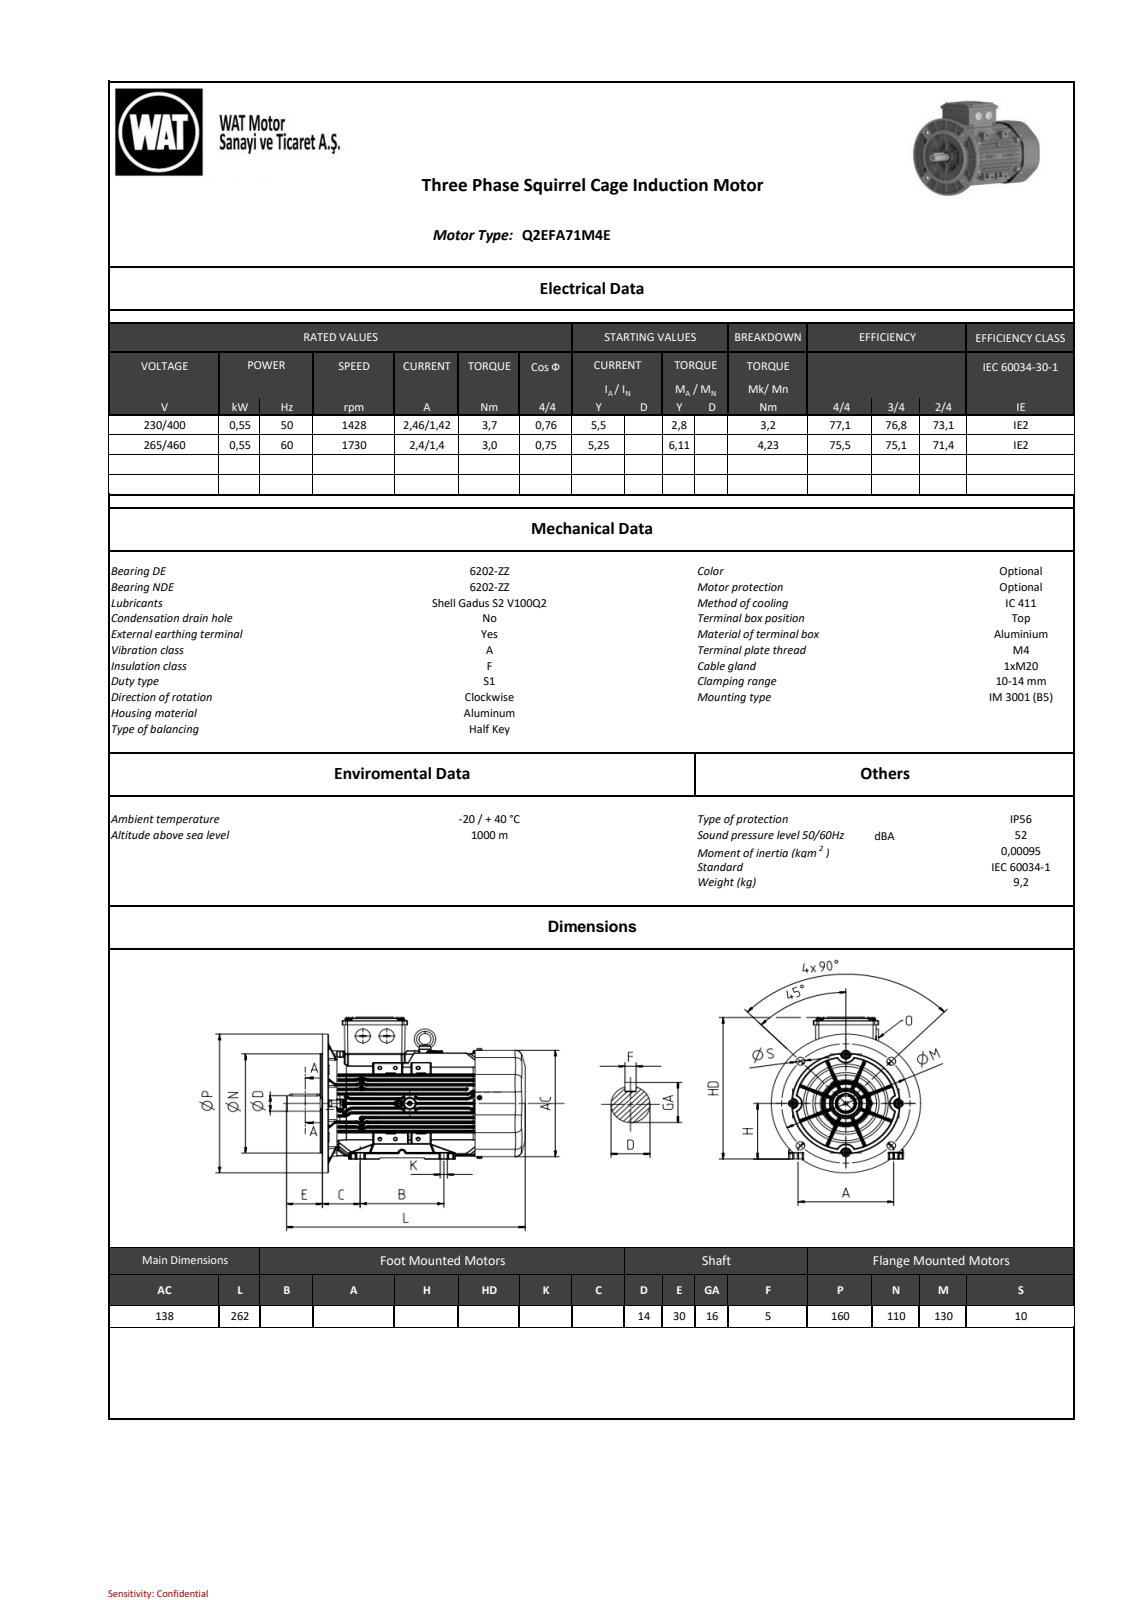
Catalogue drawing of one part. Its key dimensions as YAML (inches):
part_name: "001_objects"
step_written_by: "SIEMENS PLM Software NX2206.8101 (AUTOMOTIVE_DESIGN)"
units: inches
bodies: {solids: 0, faces: 3060, planar: 1377, cylindrical: 779, other: 904}
overall_size: [10.315, 7.367, 6.299]
round_holes:
  - {diameter: 0.13, count: 9}
  - {diameter: 0.144, count: 8}
  - {diameter: 0.098, count: 6}
  - {diameter: 0.197, count: 5}
  - {diameter: 0.157, count: 4}
  - {diameter: 0.177, count: 4}
  - {diameter: 0.183, count: 4}
  - {diameter: 0.189, count: 4}
  - {diameter: 0.394, count: 4}
  - {diameter: 0.118, count: 3}
  - {diameter: 0.146, count: 3}
  - {diameter: 0.181, count: 2}
round_bosses_or_shafts:
  - {diameter: 0.315, count: 8}
  - {diameter: 0.157, count: 8}
  - {diameter: 6.299, count: 1}
  - {diameter: 5.433, count: 1}
  - {diameter: 4.331, count: 1}
  - {diameter: 2.402, count: 1}
  - {diameter: 1.024, count: 1}
  - {diameter: 0.995, count: 1}
partial_cylinders:
  - {radius: 0.039, count: 117}
  - {radius: 0.02, count: 48}
  - {radius: 0.047, count: 36}
  - {radius: 0.394, count: 32}
  - {radius: 0.079, count: 30}
  - {radius: 0.059, count: 24}
  - {radius: 0.157, count: 23}
  - {radius: 0.03, count: 18}
face_to_face_distances: [0.079, 0.118, 0.197, 7.776, 3.268, 0.039, 7.449, 7.646, 7.657, 7.528]
hole_center_spacings: [2.417, 3.442, 3.53, 3.533, 2.165, 1.441, 2.559, 2.645]
